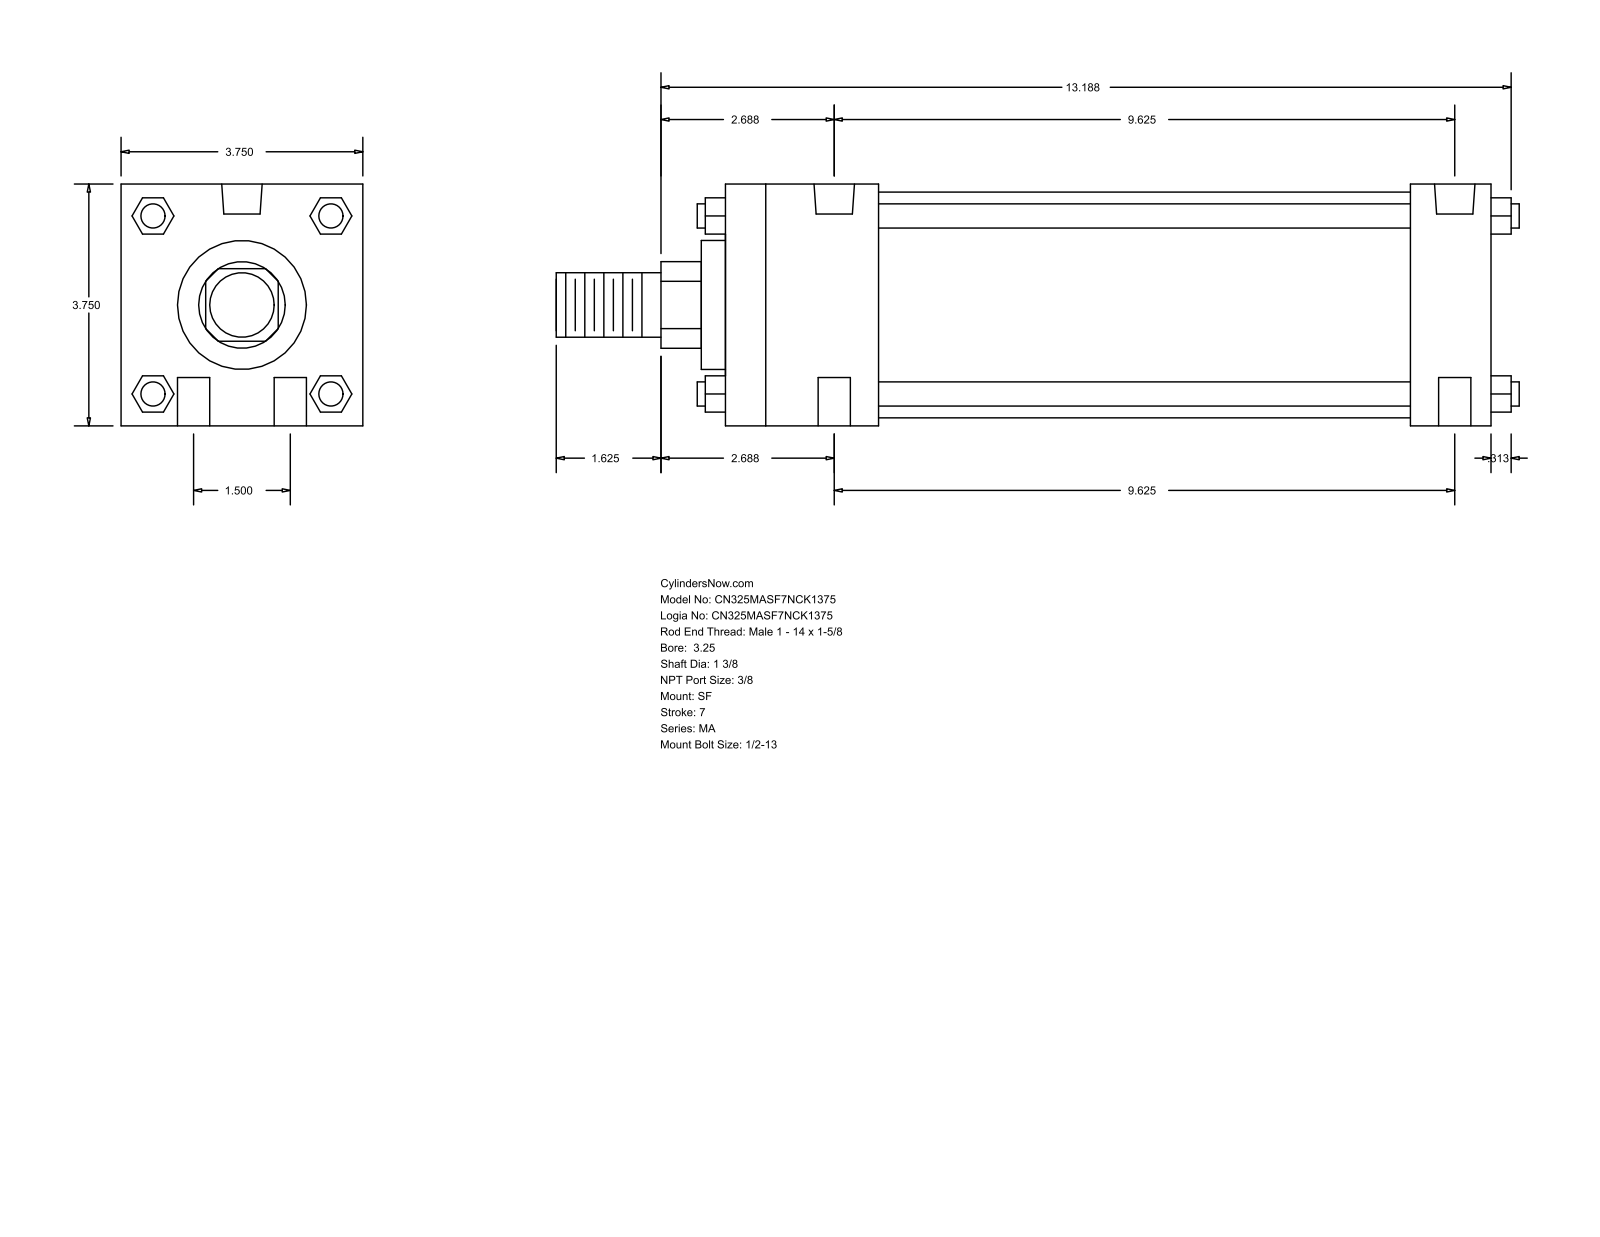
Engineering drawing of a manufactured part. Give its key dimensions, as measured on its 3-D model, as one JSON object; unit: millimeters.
{"part_name": "MA_SF__0325_1.375", "step_written_by": "GSSL Pune (CONFIG_CONTROL_DESIGN)", "units": "millimeters", "bodies": {"solids": 0, "faces": 124, "planar": 94, "cylindrical": 30, "other": 0}, "overall_size": [379.41, 95.25, 95.25], "round_holes": [[12.7, 4], [11.11, 2], [15.93, 2]], "round_bosses_or_shafts": [[9.53, 4], [88.9, 1], [50.8, 1], [34.92, 1], [25.4, 1]], "partial_cylinders_radius": [[17.06, 1]], "face_to_face_distances": [95.24, 301.62, 269.87, 31.75, 60.32, 209.55, 241.3, 9.52, 69.84, 279.39], "hole_center_spacings": [19.05, 245.22, 244.48, 38.1, 247.43, 234.95]}
